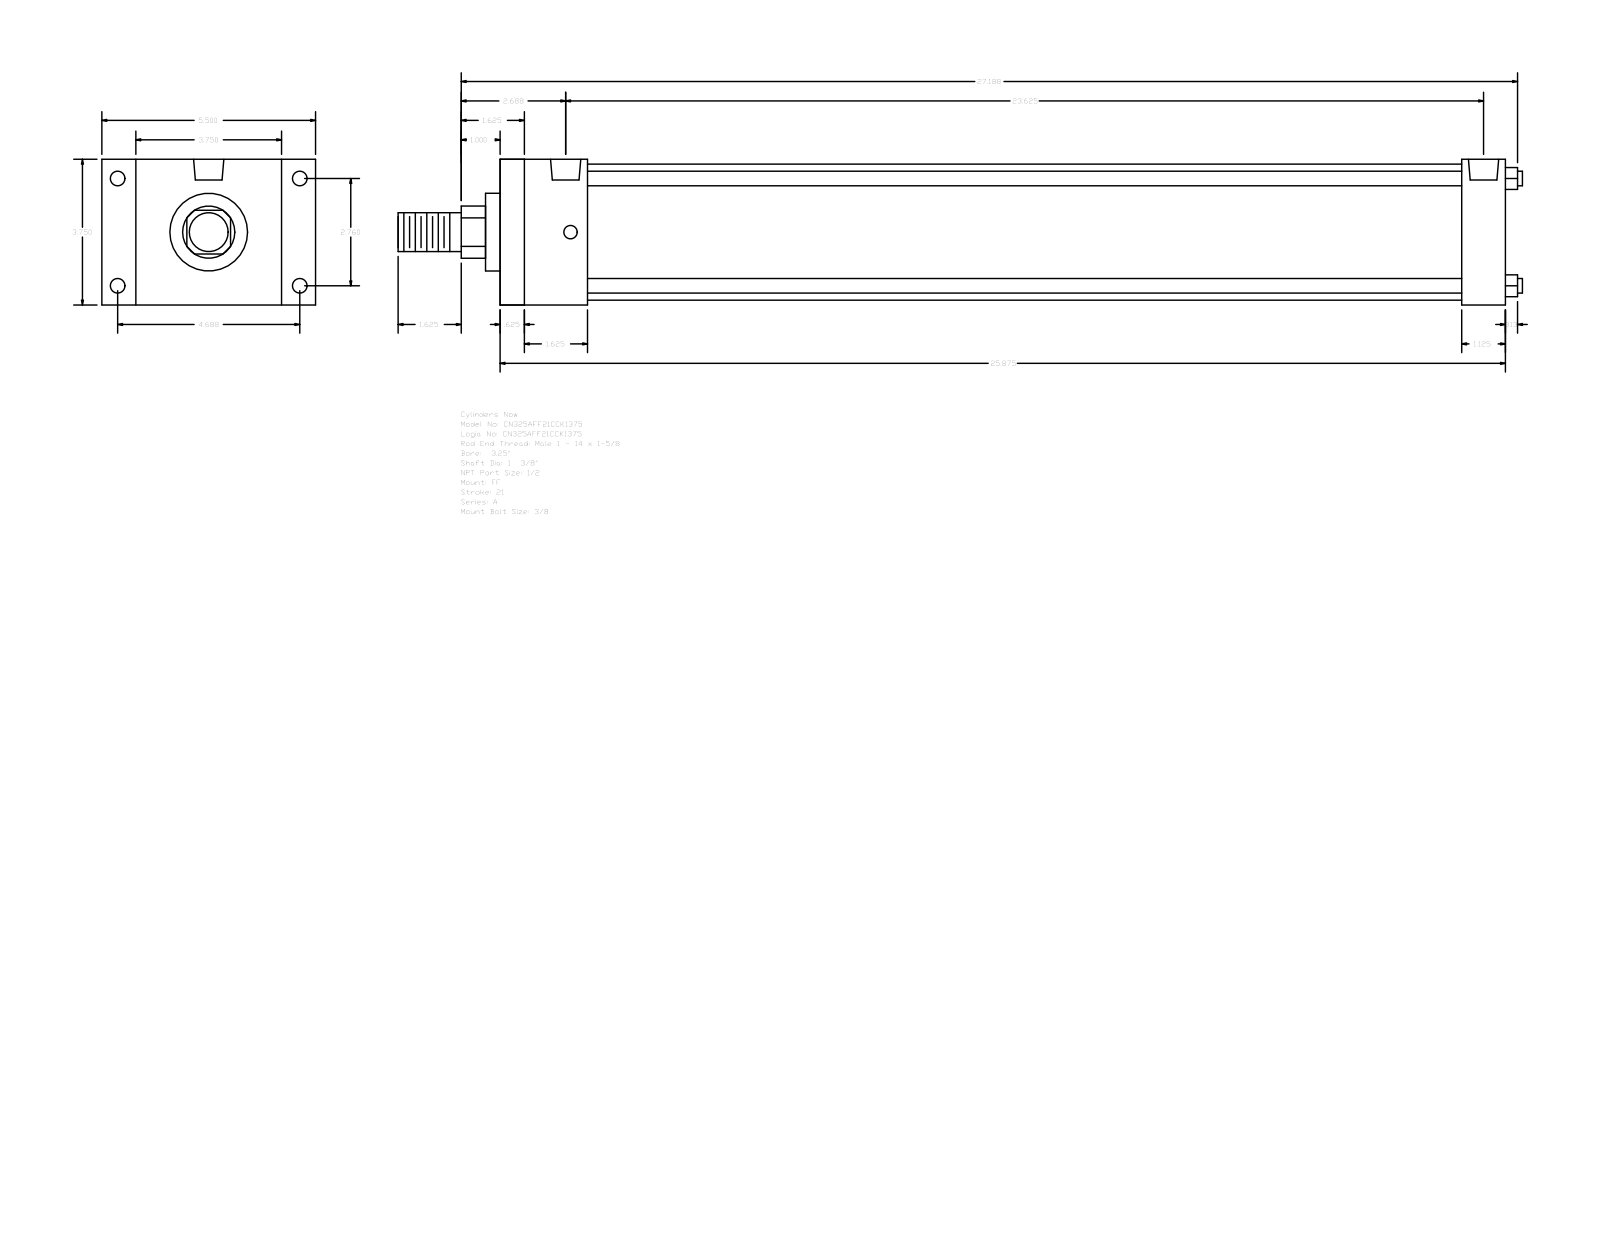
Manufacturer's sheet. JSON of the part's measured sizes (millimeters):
{"part_name": "A_FF__0325_1.375", "step_written_by": "GSSL Pune (CONFIG_CONTROL_DESIGN)", "units": "millimeters", "bodies": {"solids": 0, "faces": 92, "planar": 64, "cylindrical": 28, "other": 0}, "overall_size": [735.01, 139.7, 95.25], "round_holes": [[8.73, 4], [9.53, 4], [19.77, 2]], "round_bosses_or_shafts": [[9.53, 4], [88.9, 1], [50.8, 1], [34.92, 1], [25.4, 1]], "partial_cylinders_radius": [[17.06, 1]], "face_to_face_distances": [95.24, 657.22, 641.35, 15.87, 57.15, 22.23, 117.47, 28.57, 628.65, 41.28], "hole_center_spacings": [3.18, 70.1, 119.06, 138.16, 593.72, 596.9, 600.08]}
